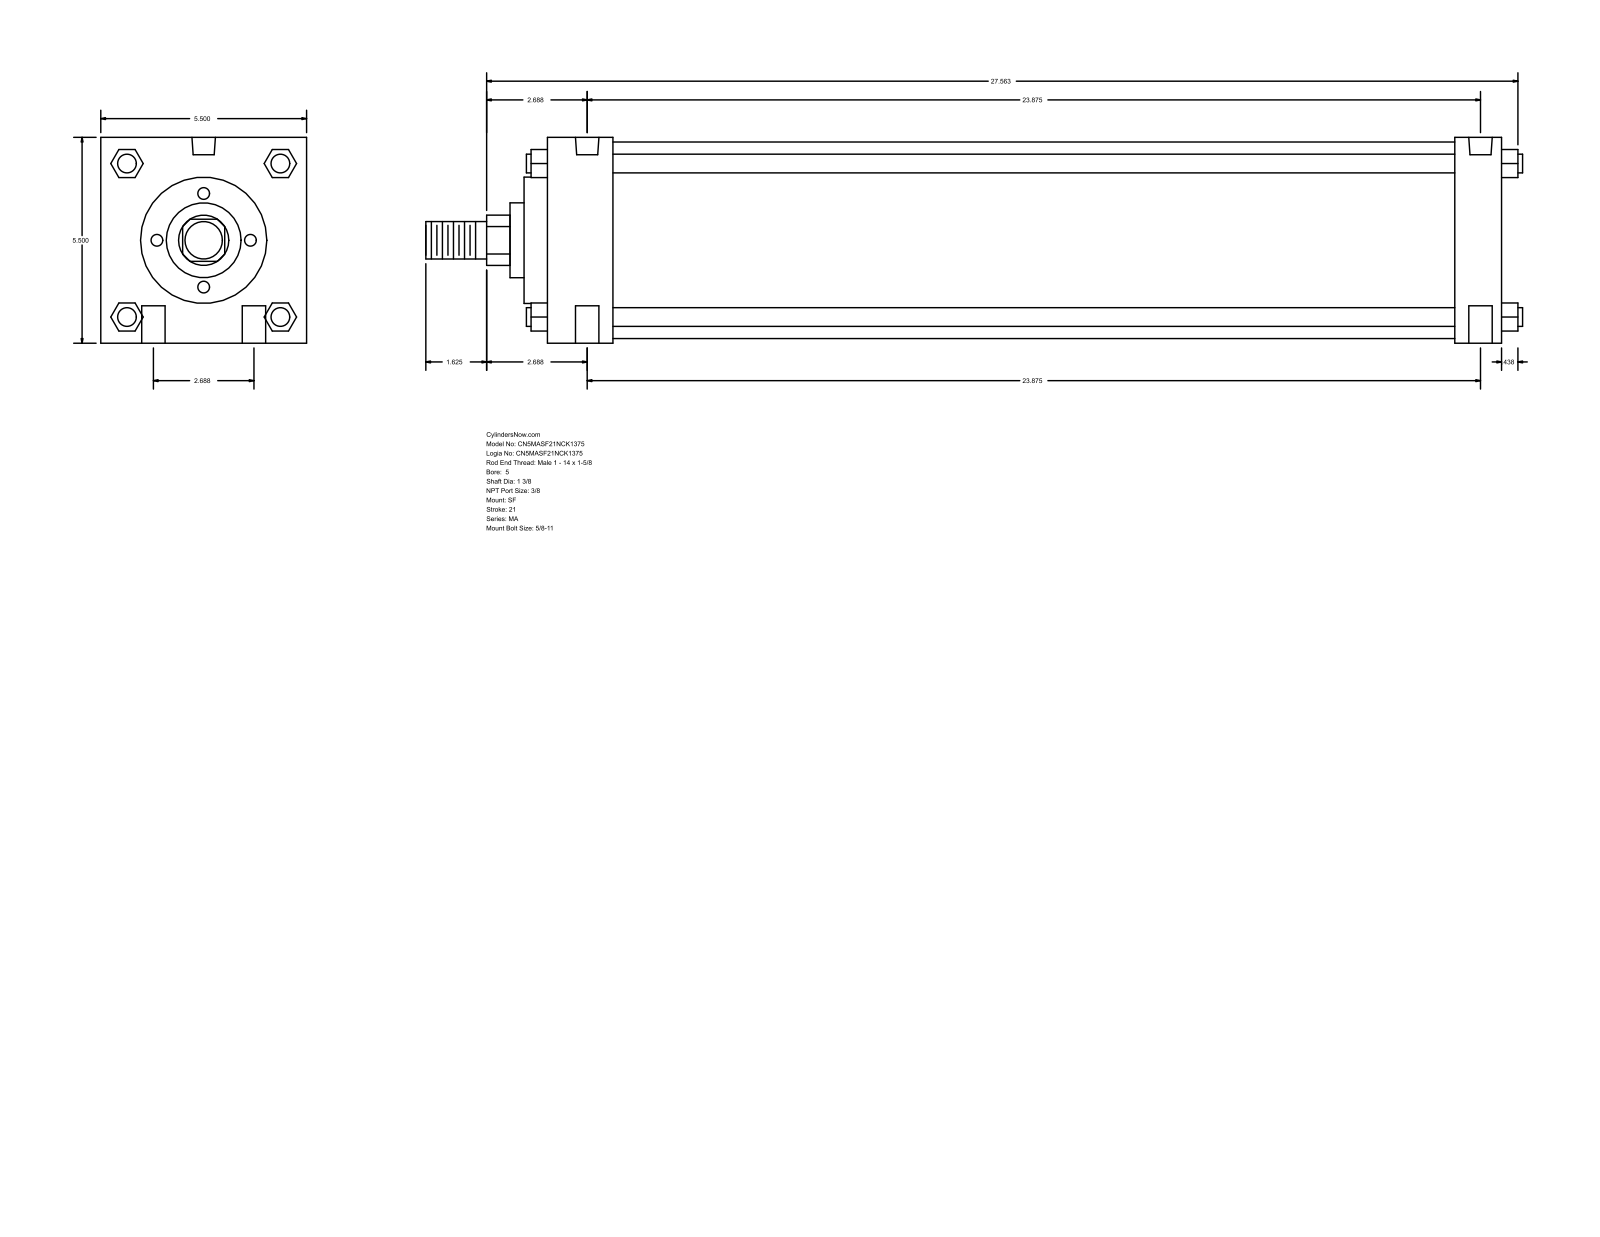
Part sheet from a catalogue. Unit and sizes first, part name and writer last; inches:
Units: inches
Overall size (bounding box): 29.313 × 5.5 × 5.5
Round holes (diameter × count): ⌀0.625 ×4, ⌀0.437 ×2, ⌀0.627 ×2
Round bosses / shafts (diameter × count): ⌀0.5 ×4, ⌀5.25 ×1, ⌀3.375 ×1, ⌀2 ×1, ⌀1.375 ×1, ⌀1 ×1
Partial cylindrical surfaces — rounded edges, fillets, slot ends (radius × count): R0.672 ×1
Main face-to-face distances: 5.5, 25.5, 1.75, 24.25, 22.5, 23.75, 1.25, 0.625, 2.375, 24.875
Hole centre spacings: 1.344, 23.913, 23.875, 2.687, 24.026, 23.5
Bodies: 0 solids, 126 faces (95 planar, 31 cylindrical, 0 other)
Part name (STEP PRODUCT): MA_SF__0500_1.375
STEP written by: GSSL Pune (CONFIG_CONTROL_DESIGN)
